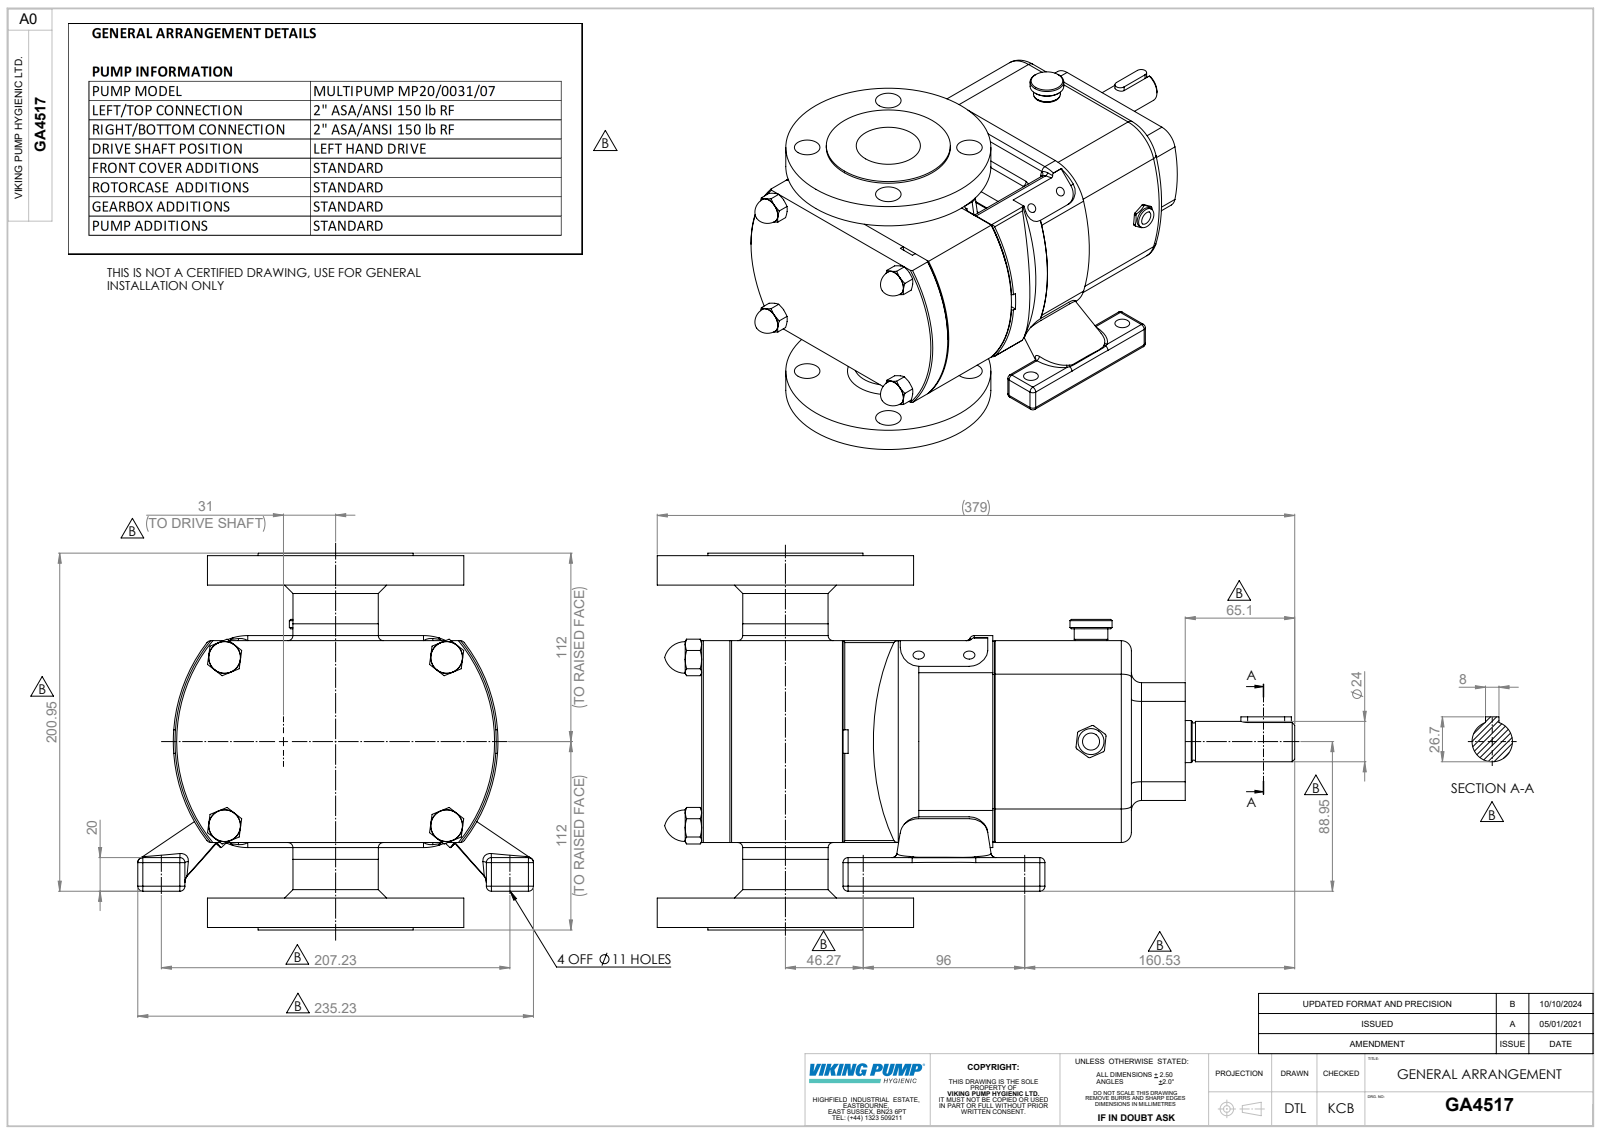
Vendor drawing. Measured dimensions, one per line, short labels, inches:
name: Copy of CP20-0031-07 V L^GA4517; GA4517; Copy of Z94-5301-33 - 2 INCH ASA 150^GA4517
written by: SolidWorks 2023 (AUTOMOTIVE_DESIGN)
unit: in
bodies: 3 solids, 821 faces (252 planar, 302 cylindrical, 267 other)
size: 14.921 × 9.261 × 8.819
volume: 351.1 in³; area: 619 in²
holes: 6× ⌀0.748, 4× ⌀0.268, 4× ⌀0.433, 3× ⌀0.255, 2× ⌀0.315, 1× ⌀0.887, 1× ⌀1.878
bosses: 2× ⌀1.378, 1× ⌀6, 1× ⌀3.63, 1× ⌀2, 1× ⌀1.996, 1× ⌀0.985, 1× ⌀0.984, 1× ⌀0.945
rounds: 60× R0.118, 18× R0.079, 16× R0.039, 8× R0.236, 8× R0.437, 6× R0.05, 6× R0.157, 6× R0.315
face distances: 1.299, 6.024, 0.689, 1.988, 6.713, 8.012, 4.724, 7.323, 8.701, 0.059
hole spacings: 2.374, 3.357, 4.748, 2.114, 1.183, 2.405, 3.356, 3.359
